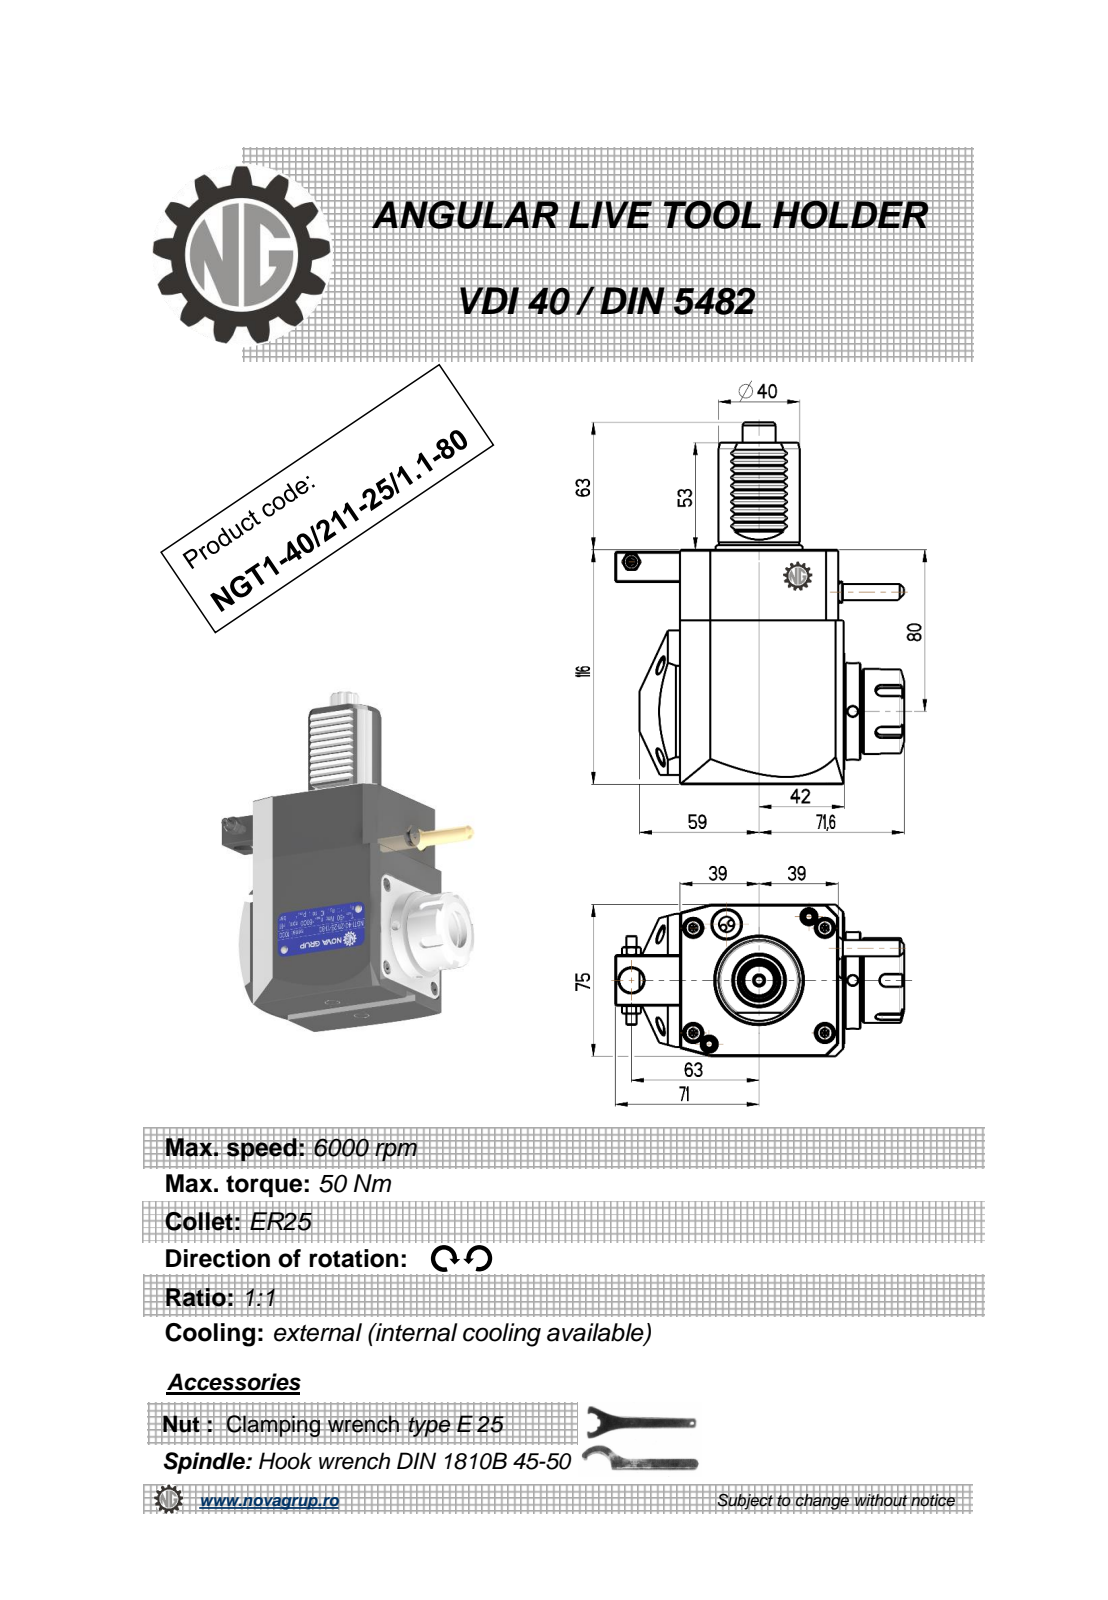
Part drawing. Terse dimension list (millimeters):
name: NGT1_40_211_25_1_1_80
written by: PRO/ENGINEER BY PARAMETRIC TECHNOLOGY CORPORATION, 2010280 (CONFIG_CONTROL_DESIGN)
unit: mm
bodies: 1 solid, 480 faces (190 planar, 124 cylindrical, 166 other)
size: 179 × 142.6 × 76.6
volume: 852 338 mm³; area: 69 023 mm²
holes: 3× ⌀5, 2× ⌀4.2, 1× ⌀3, 1× ⌀9.5, 1× ⌀12, 1× ⌀20.3
bosses: 1× ⌀48, 1× ⌀42, 1× ⌀40, 1× ⌀37.5, 1× ⌀33, 1× ⌀11.2, 1× ⌀8.96, 1× ⌀8
rounds: 18× R3.03, 12× R0.26, 10× R0.3, 6× R0.22, 5× R3, 1× R0.5, 1× R6.75, 1× R8.22
face distances: 75, 116, 81, 3, 78, 80.8, 2.8, 25, 7.5, 11
hole spacings: 20.93, 46.25, 61.13, 63, 72.5, 109.25, 131.95
